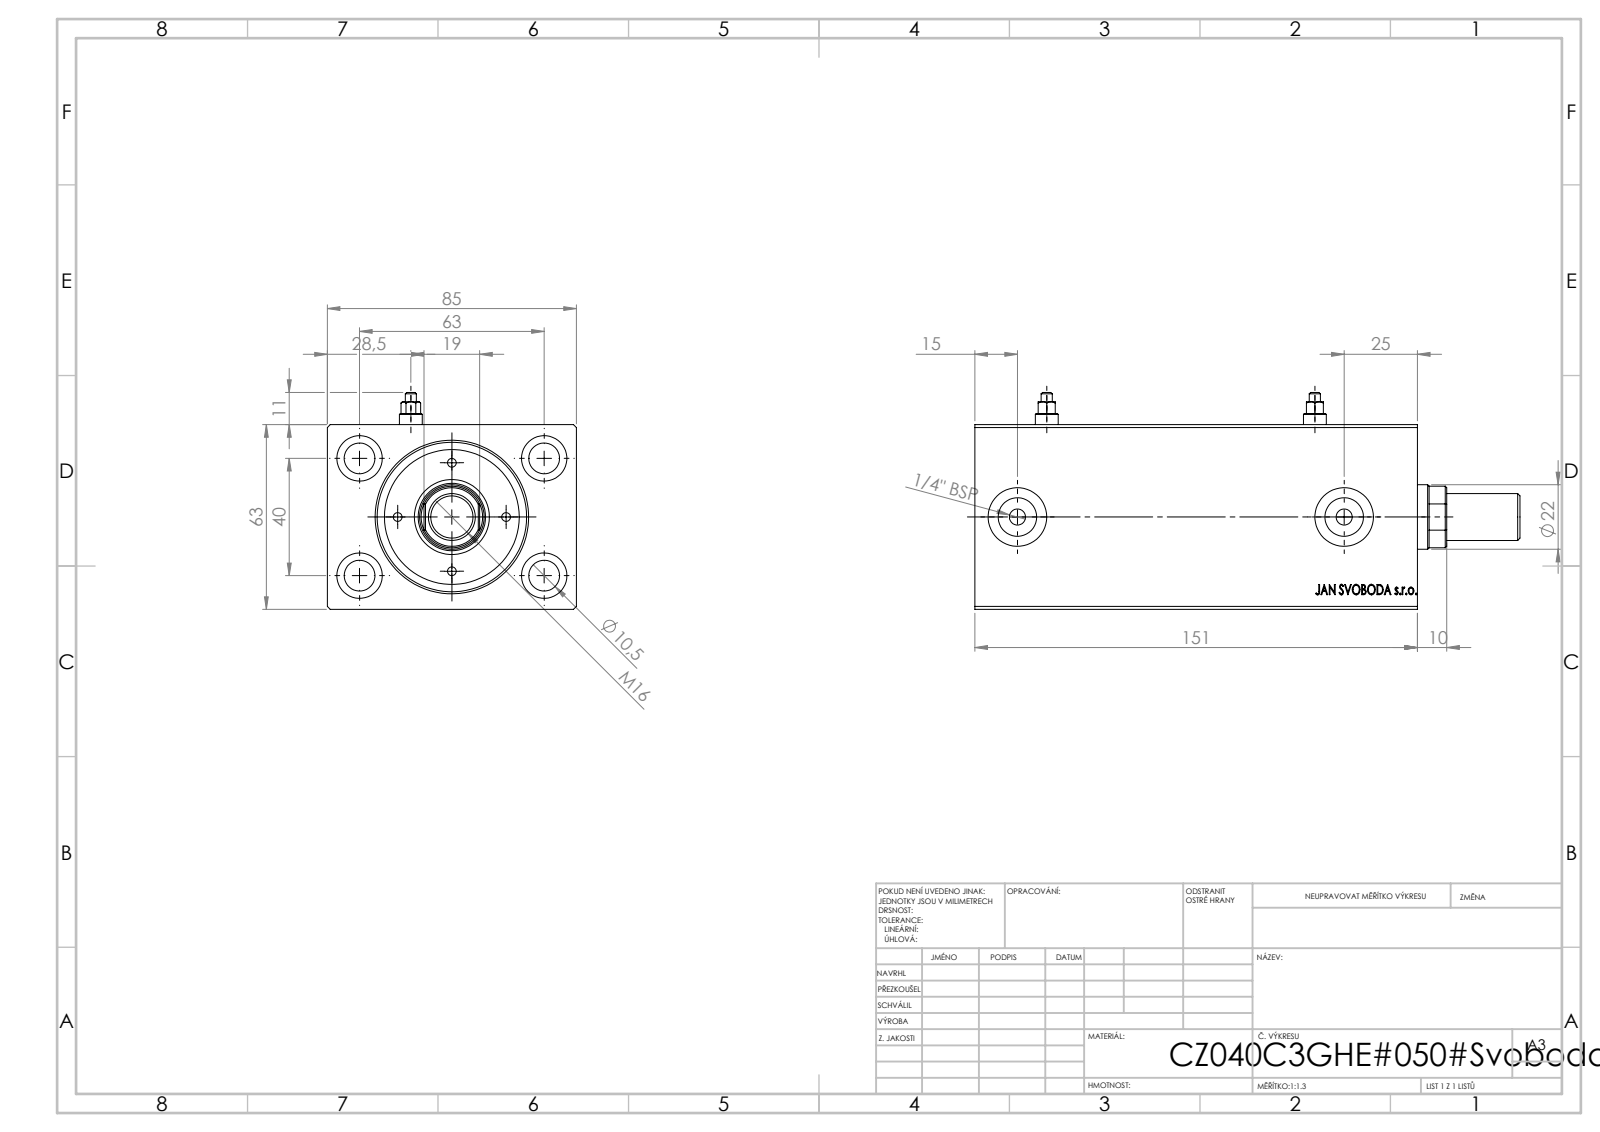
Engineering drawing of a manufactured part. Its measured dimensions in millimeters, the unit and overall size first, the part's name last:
Units: millimetres
Overall size (bounding box): 151 × 85 × 63
Round holes (diameter × count): ⌀10.5 ×4, ⌀15.5 ×4, ⌀5.5 ×2, ⌀8 ×2, ⌀13.16 ×2, ⌀20 ×2, ⌀36 ×1, ⌀40 ×1, ⌀51 ×1
Main face-to-face distances: 63, 85, 151, 135.7, 15.3, 150.8, 15.1, 10.33, 140.67, 10
Hole centre spacings: 37.31, 40, 63, 74.63, 91.5, 111.5
Volume: 564 754 mm³ · Surface area: 94 504 mm²
Bodies: 1 solid, 825 faces (397 planar, 46 cylindrical, 382 other)
STEP written by: SolidWorks 2019 (CONFIG_CONTROL_DESIGN)
